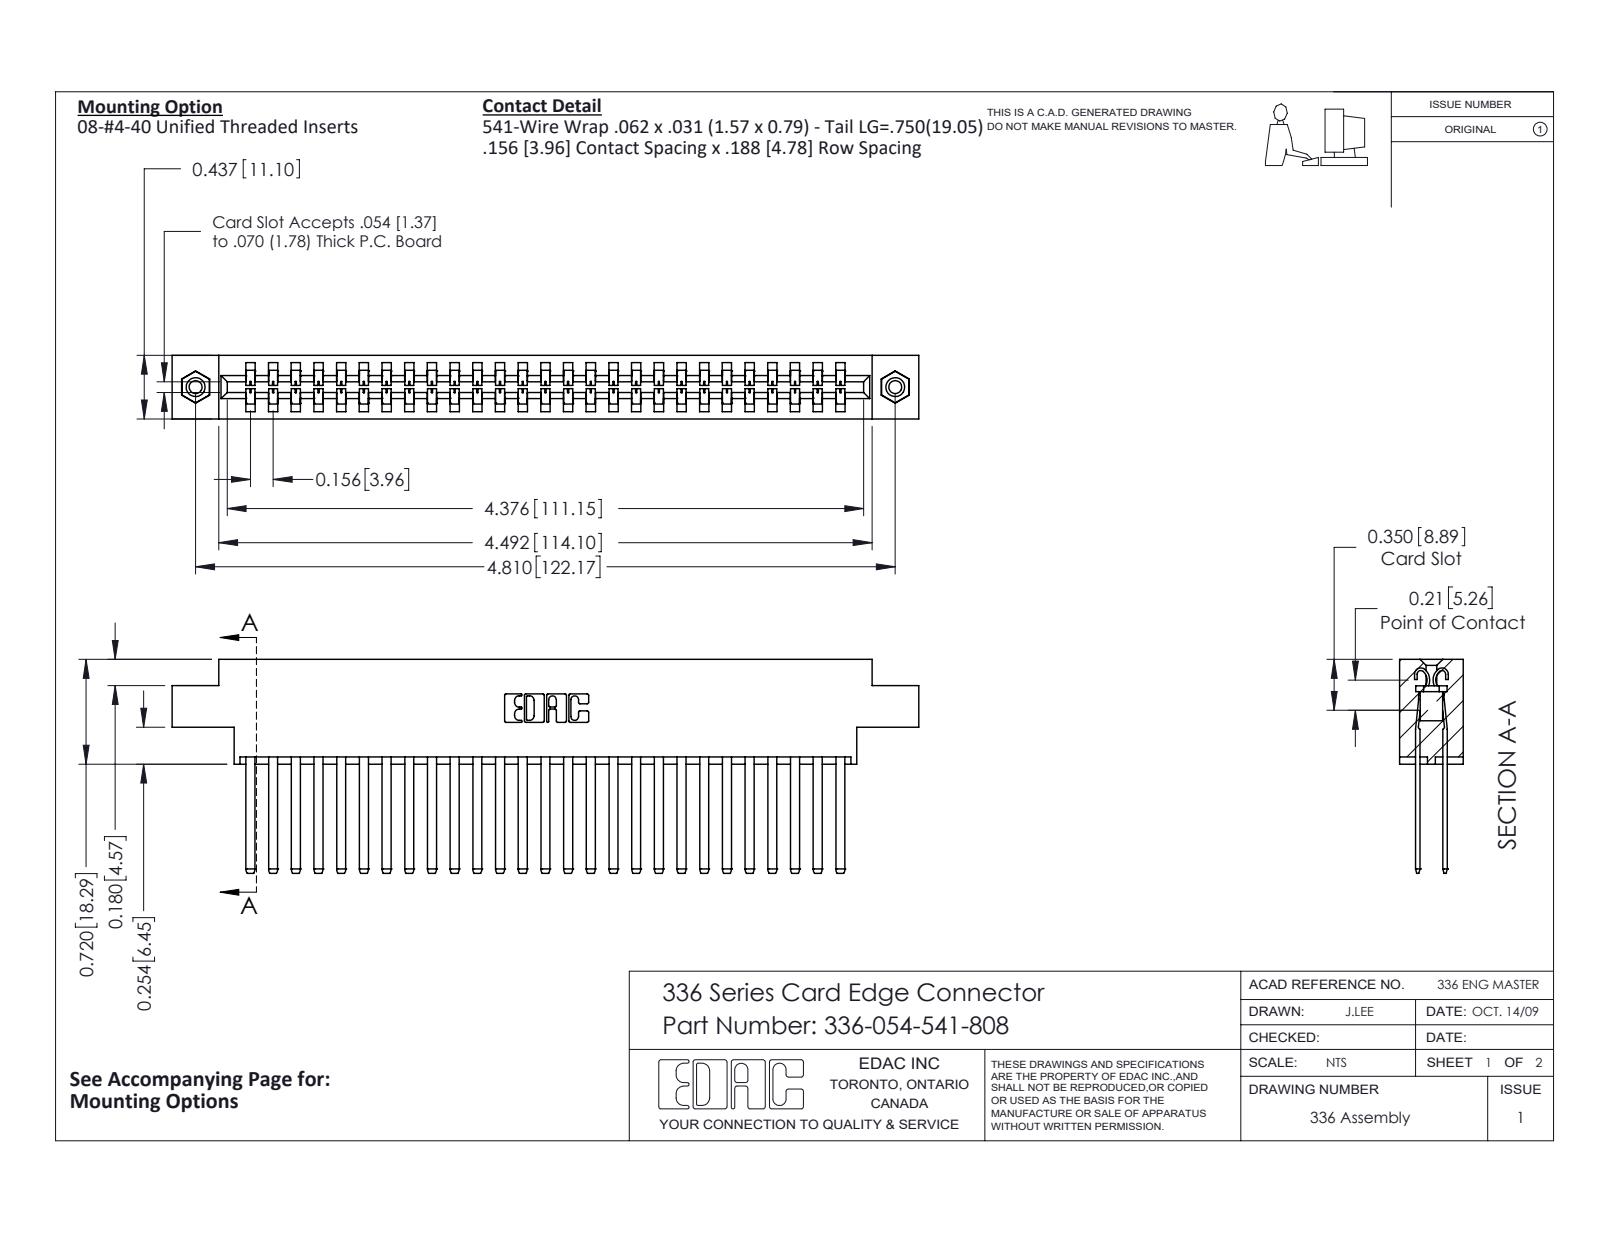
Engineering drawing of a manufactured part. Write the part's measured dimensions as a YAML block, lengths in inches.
part_name: "336-290-001_336-290-541; 345-250-001_345-250-003-102; 336 Part_Offset - .156 Dia - TI; 336-054-541-808"
step_written_by: "SolidWorks 2020 (CONFIG_CONTROL_DESIGN)"
units: inches
bodies: {solids: 57, faces: 2446, planar: 1510, cylindrical: 920, other: 16}
overall_size: [5.133, 1.47, 0.437]
volume: 1.199
surface_area: 38.67
round_holes:
  - {diameter: 0.089, count: 2}
  - {diameter: 0.125, count: 2}
  - {diameter: 0.156, count: 2}
round_bosses_or_shafts:
  - {diameter: 0.155, count: 2}
partial_cylinders:
  - {radius: 0.004, count: 108}
  - {radius: 0.056, count: 54}
  - {radius: 0.01, count: 22}
  - {radius: 0.007, count: 6}
  - {radius: 0.031, count: 6}
  - {radius: 0.022, count: 4}
  - {radius: 0.04, count: 4}
  - {radius: 0.026, count: 3}
face_to_face_distances: [0.188, 0.328, 0.14, 0.297, 0.109, 0.031, 0.437, 0.033, 0.181, 0.146]
hole_center_spacings: [4.81]
